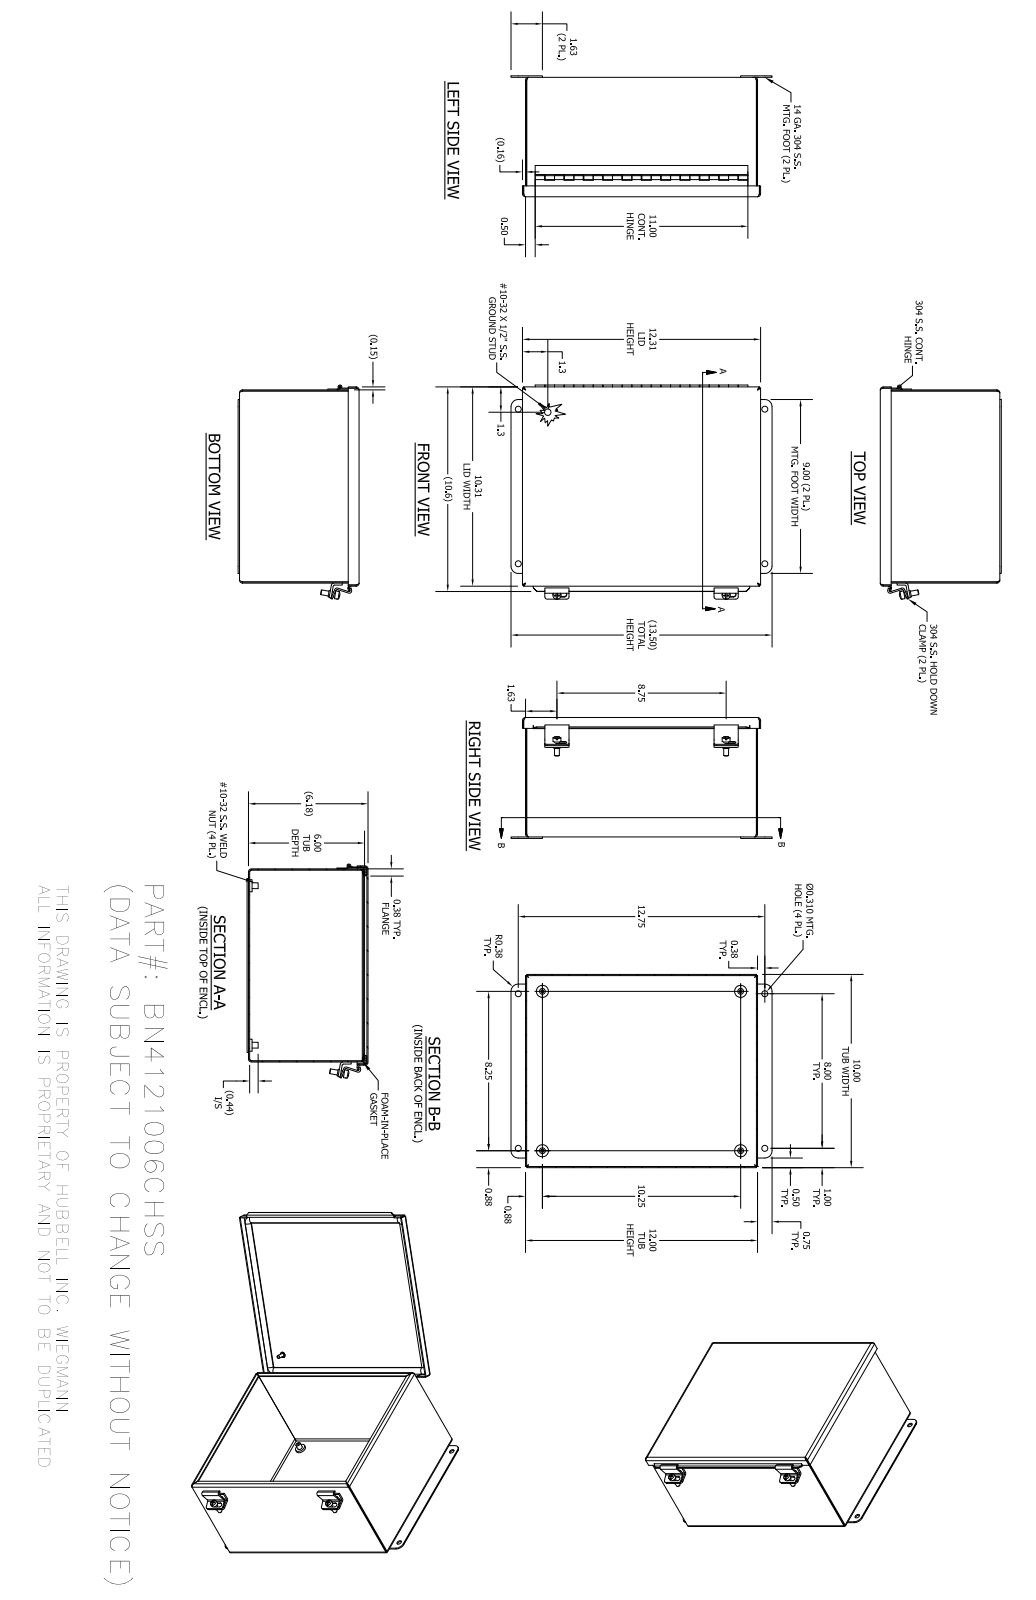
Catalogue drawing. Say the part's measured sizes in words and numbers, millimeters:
The part is named "B_121006_SSBKP; H4050551LH; H4050551P; H4050551TH (+8 more)". Its 3-D file was written by "Autodesk Inventor 2016 (AUTOMOTIVE_DESIGN)". It is 19 solids with 468 faces: 256 planar, 145 cylindrical and 67 other. Overall it measures 342.9 by 281.58 by 158.91 millimeters. Its volume is 643 683 cubic millimeters and its surface area 812 696 square millimeters. Round holes: 4 of diameter 2.79, 4 of diameter 3.96, 4 of diameter 7.87, 2 of diameter 4.98, 1 of diameter 2.96. Round bosses or shafts: 4 of diameter 15.88, 4 of diameter 7.62, 2 of diameter 10.4, 2 of diameter 8.74, 2 of diameter 6.35, 1 of diameter 8.56, 1 of diameter 5.08, 1 of diameter 4.83. Partial cylindrical surfaces (rounded edges, fillets, slot ends): 13 of radius 2.38, 13 of radius 3.88, 8 of radius 1.68, 8 of radius 3.17, 4 of radius 3.38, 4 of radius 5.78, 4 of radius 9.53, 3 of radius 1.6. The main face-to-face distances are 1.5, 155.51, 252.5, 157.01, 154.01, 303.3, 254, 251, 304.8, 301.8. The hole center spacings are 31.91, 203.2, 222.25, 292.12, 357.65, 19.05, 208.8, 208.81.
